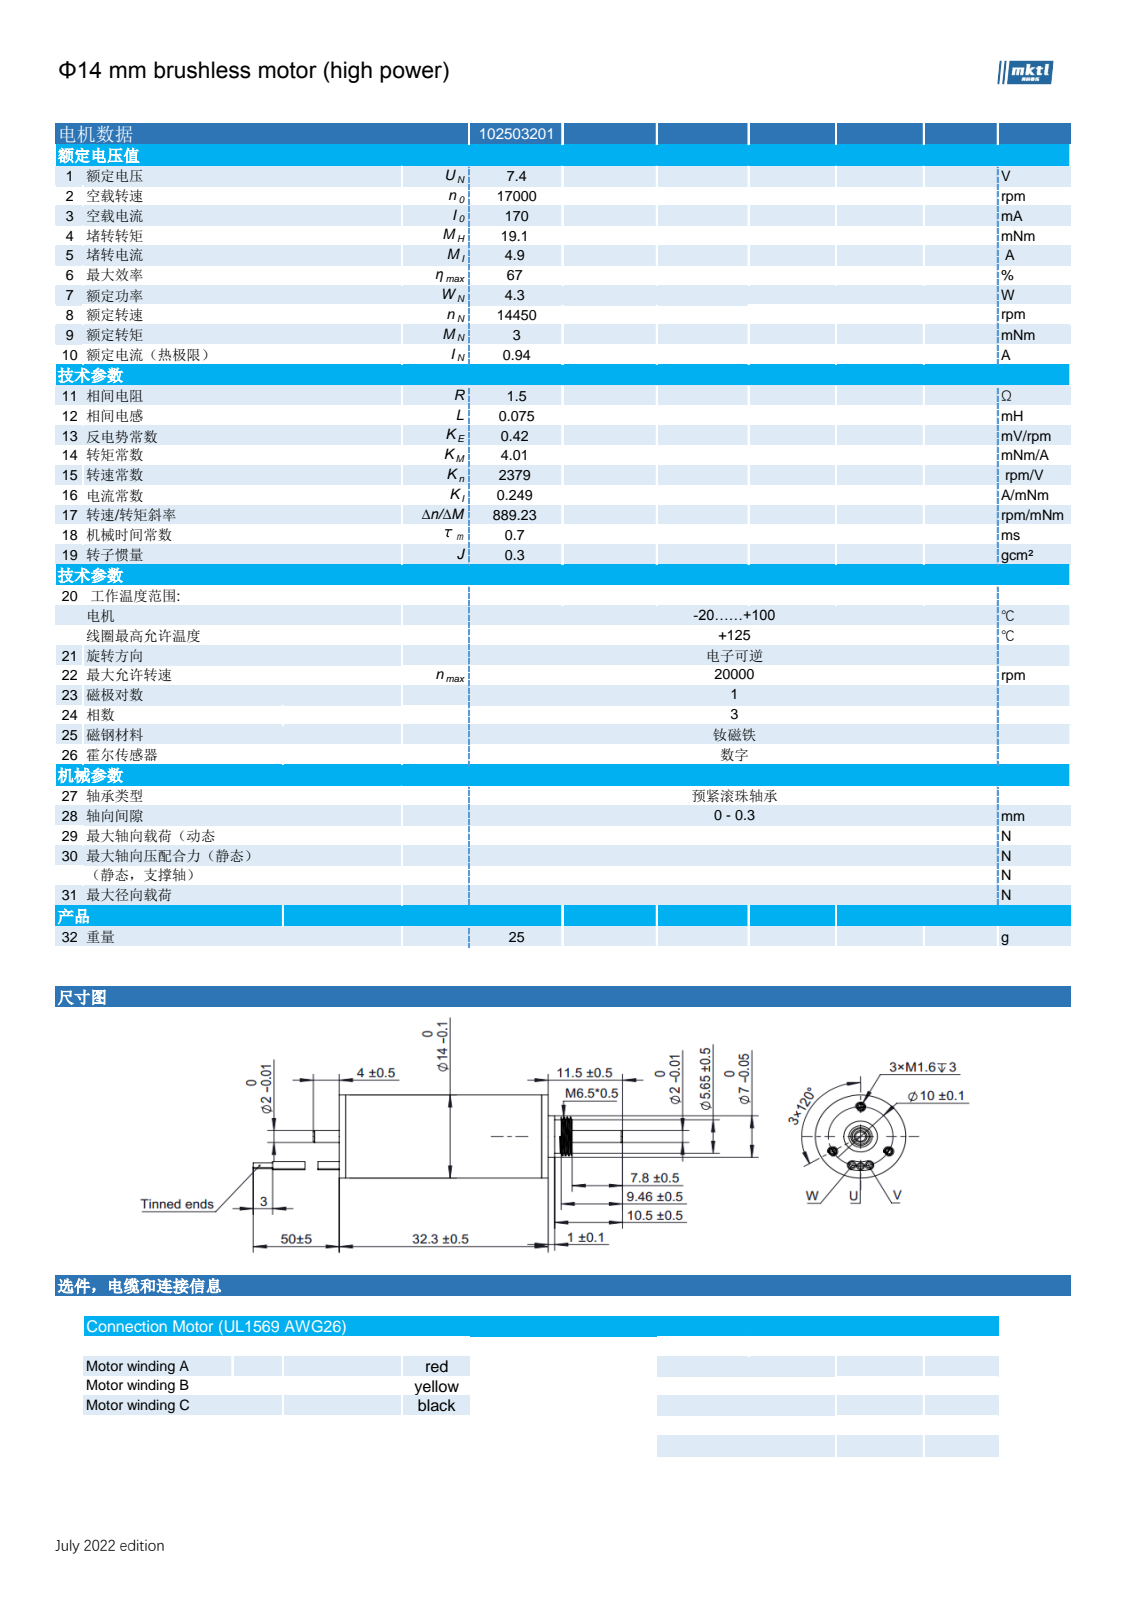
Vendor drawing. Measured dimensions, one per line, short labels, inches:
name: approval 102503201
written by: SolidWorks 2025 (AUTOMOTIVE_DESIGN)
unit: in
bodies: 140 solids, 992 faces (313 planar, 626 cylindrical, 53 other)
size: 2.248 × 0.551 × 0.551
volume: 0.279 in³; area: 34.92 in²
holes: 6× ⌀0.031, 3× ⌀0.043, 3× ⌀0.047, 3× ⌀0.049, 1× ⌀0.118, 1× ⌀0.157, 1× ⌀0.197, 1× ⌀0.205, 1× ⌀0.236, 1× ⌀0.276, 1× ⌀0.28, 1× ⌀0.386
bosses: 3× ⌀0.047, 3× ⌀0.023, 1× ⌀0.551, 1× ⌀0.52, 1× ⌀0.517, 1× ⌀0.516, 1× ⌀0.26, 1× ⌀0.256
rounds: 2× R0.03, 1× R0.167, 1× R0.226
face distances: 0.016, 0.024, 0.031, 0.039, 0.047, 0.055, 0.063, 0.071, 0.079, 0.087
hole spacings: 0.197, 0.341, 0.051, 0.151, 0.239, 0.39, 0.102, 0.394
